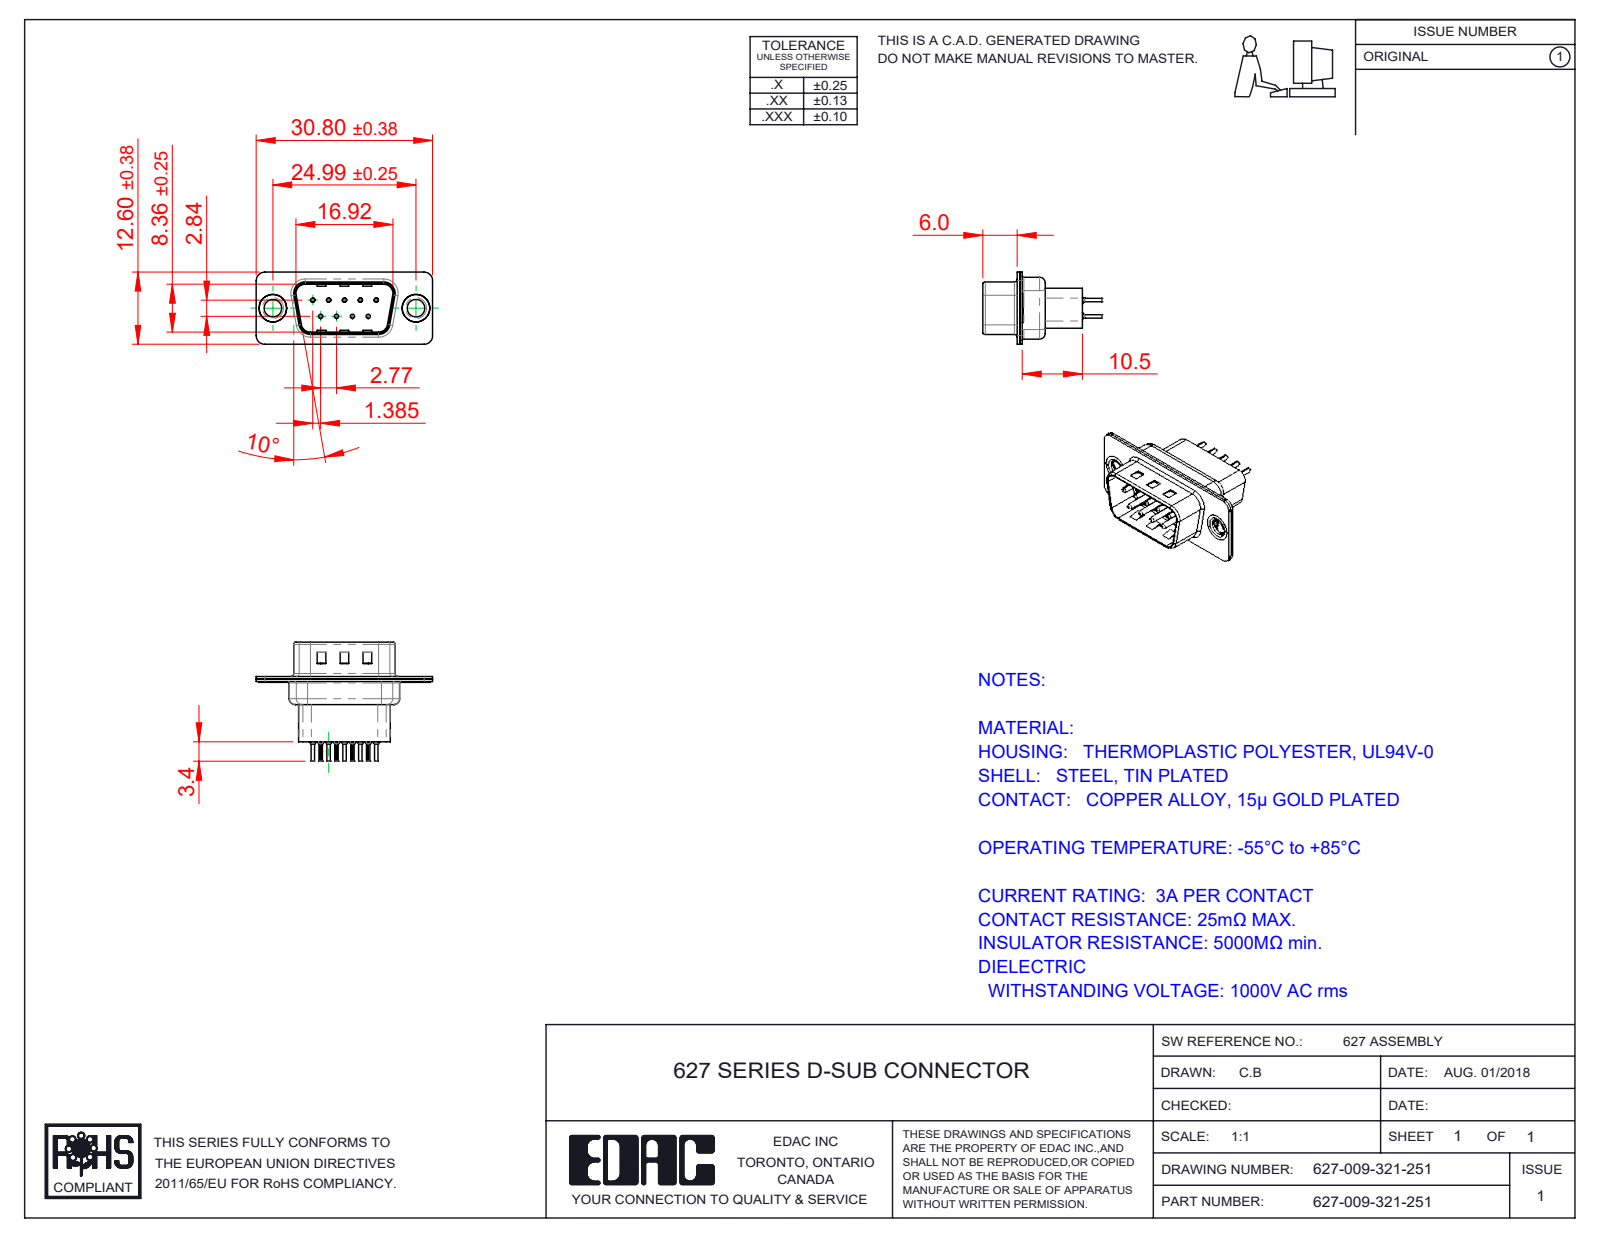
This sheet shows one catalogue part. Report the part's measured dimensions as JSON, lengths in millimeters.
{"part_name": "627 Housing_09 HP; 627 Thru Hole Rivet; 627 Shell Rear_09 Contacts; 627 Shell Front_09 Contacts (+3 more)", "step_written_by": "SolidWorks 2020 (CONFIG_CONTROL_DESIGN)", "units": "millimeters", "bodies": {"solids": 14, "faces": 1160, "planar": 323, "cylindrical": 446, "other": 391}, "overall_size": [30.8, 20.8, 12.6], "volume_mm3": 1694, "surface_area_mm2": 4554, "round_holes": [[0.2, 9], [0.35, 9], [1.1, 9], [1.6, 9], [3.05, 2], [4, 2], [4.8, 2]], "round_bosses_or_shafts": [[2, 9], [1.5, 9], [0.75, 9], [0.6, 9], [5, 2], [4.9, 2], [3.55, 2]], "partial_cylinders_radius": [[0.1, 18], [1.5, 18], [2, 12], [0.5, 8], [1.6, 8], [0.25, 4], [0.6, 4], [0.65, 4]], "face_to_face_distances": [0.45, 0.4, 0.9, 0.82, 9.58, 1.4, 1.5, 0.68, 7.68, 1.08], "hole_center_spacings": [3.16, 2.77, 5.54, 5.03, 5.04, 8.31, 7.48, 7.49]}
